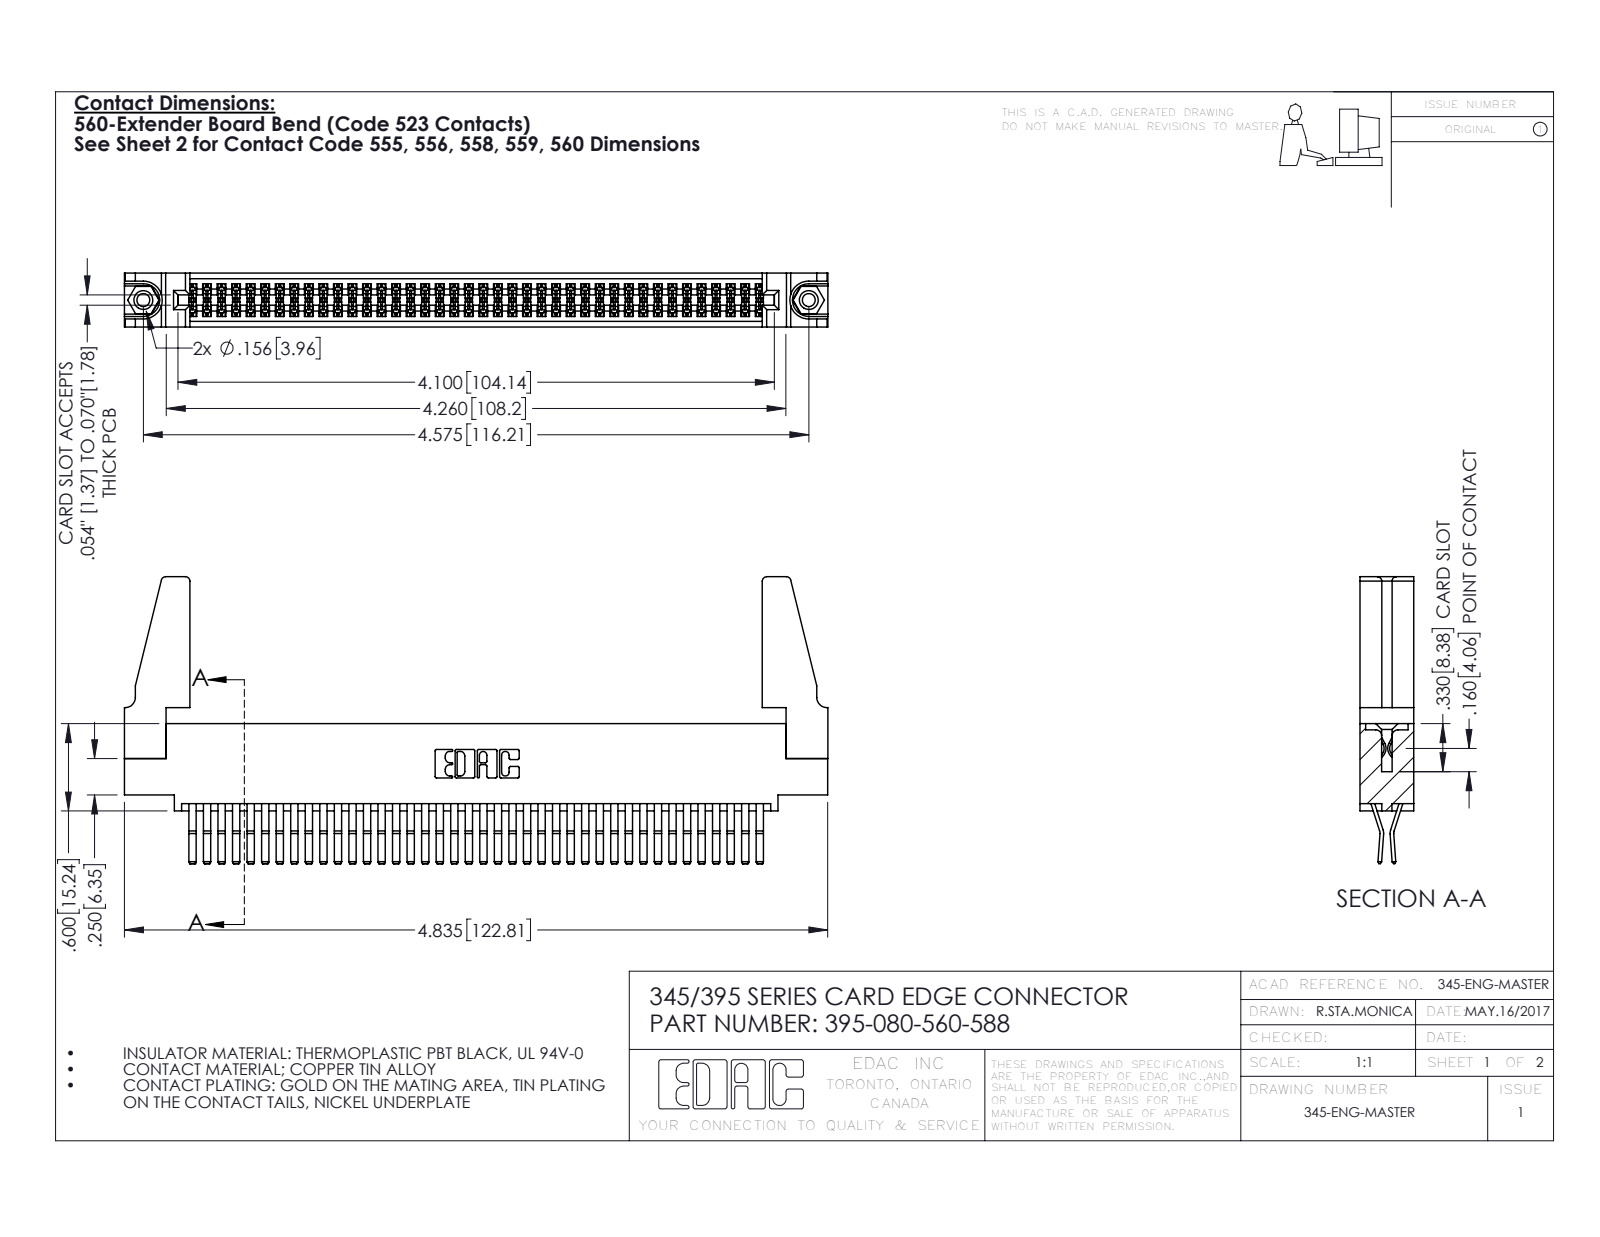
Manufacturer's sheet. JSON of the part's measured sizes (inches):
{"part_name": "395-080-560-588; 345 Part_0.110 Offset - 0.156 Dia-TH; 345-292-001_560 Tail; 345-250-001_345-250-001-102 (+1 more)", "step_written_by": "SolidWorks 2016 (CONFIG_CONTROL_DESIGN)", "units": "inches", "bodies": {"solids": 85, "faces": 4414, "planar": 2796, "cylindrical": 1602, "other": 16}, "overall_size": [4.836, 1.972, 0.37], "volume_in3": 0.953, "surface_area_in2": 35.34, "round_holes": [[0.089, 2], [0.125, 2], [0.156, 2], [0.064, 1]], "round_bosses_or_shafts": [[0.155, 2]], "partial_cylinders_radius": [[0.006, 120], [0.01, 22], [0.03, 8], [0.007, 6], [0.031, 6], [0.026, 3], [0.01, 2], [0.014, 2]], "face_to_face_distances": [0.072, 0.298, 0.025, 0.37, 0.2, 0.098, 0.272, 0.225, 0.175, 0.149], "hole_center_spacings": [0.27, 4.339, 4.575]}
